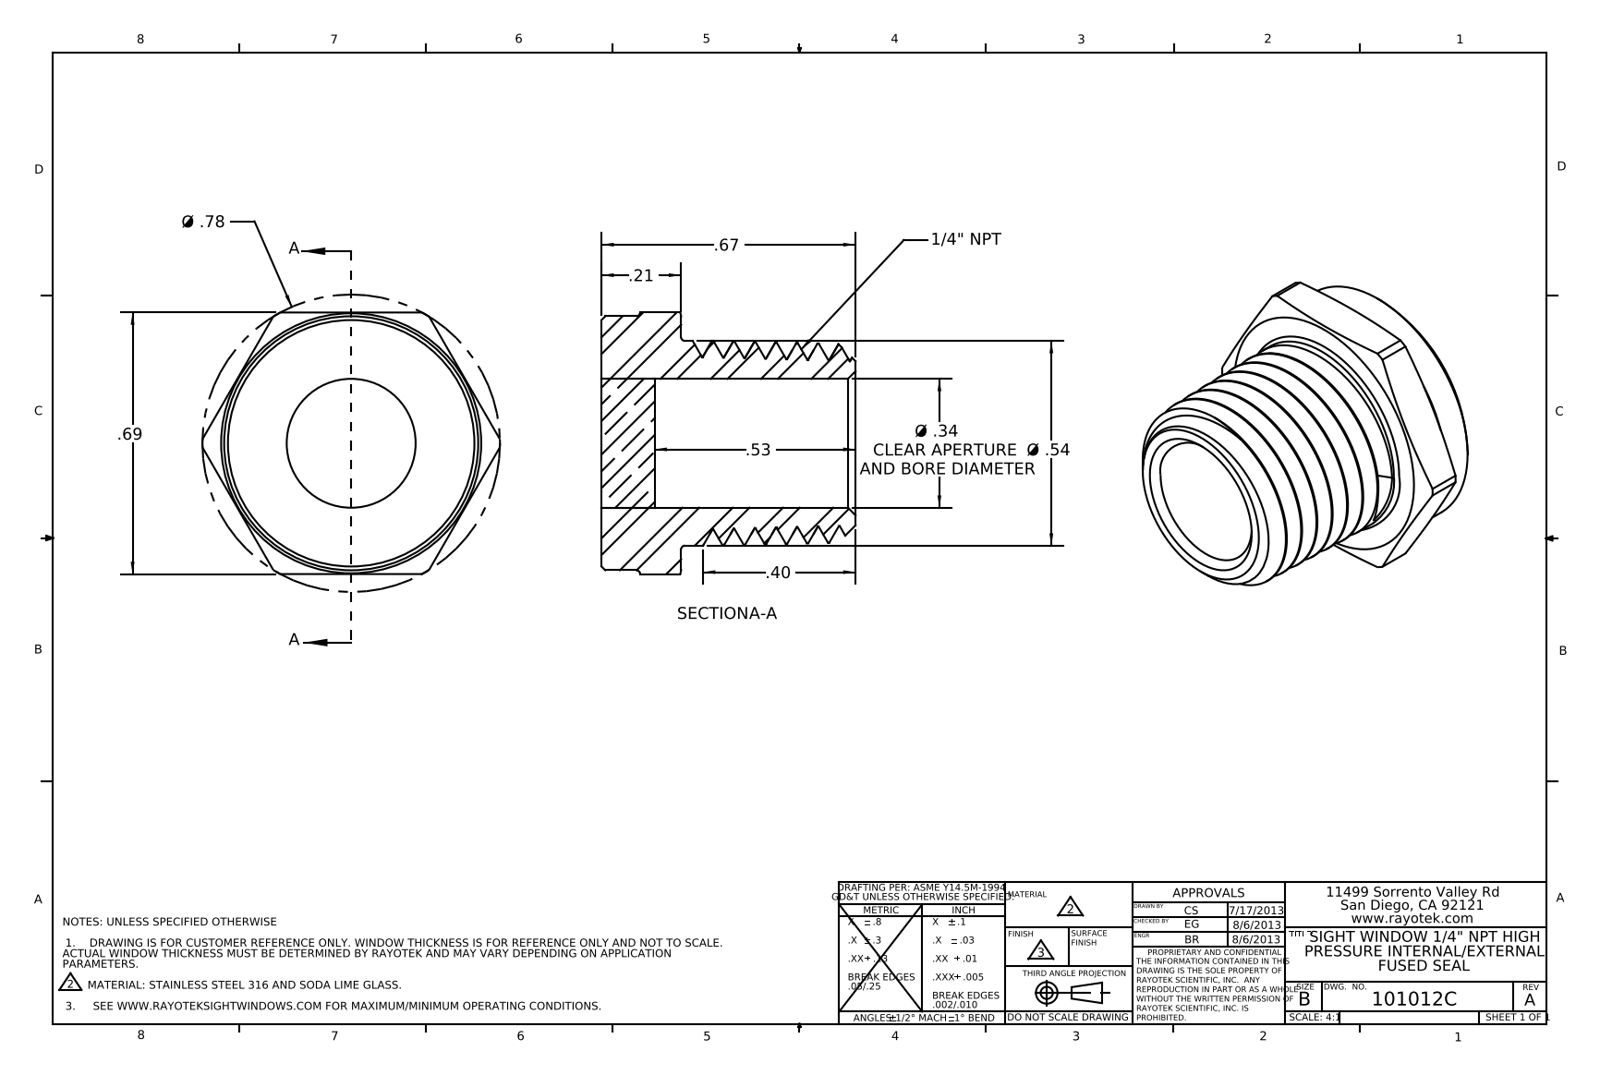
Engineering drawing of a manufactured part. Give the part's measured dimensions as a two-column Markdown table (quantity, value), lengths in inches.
| quantity | value |
| --- | --- |
| part name | 101012; 402012; 403012_CUTOMER |
| STEP written by | SolidWorks 2012 (AUTOMOTIVE_DESIGN) |
| units | inches |
| bodies | 2 solids, 61 faces (14 planar, 16 cylindrical, 31 other) |
| overall size | 0.785 × 0.69 × 0.67 |
| volume | 0.12 in³ |
| surface area | 3.29 in² |
| round holes (diameter × count) | 0.34 × 1 |
| round bosses / shafts (diameter × count) | 0.67 × 1, 0.54 × 1 |
| partial cylindrical surfaces (radius × count) | 0.392 × 1 |
| main face-to-face distances | 0.69, 0.21, 0.14, 0.07, 0.67, 0.53, 0.46 |
